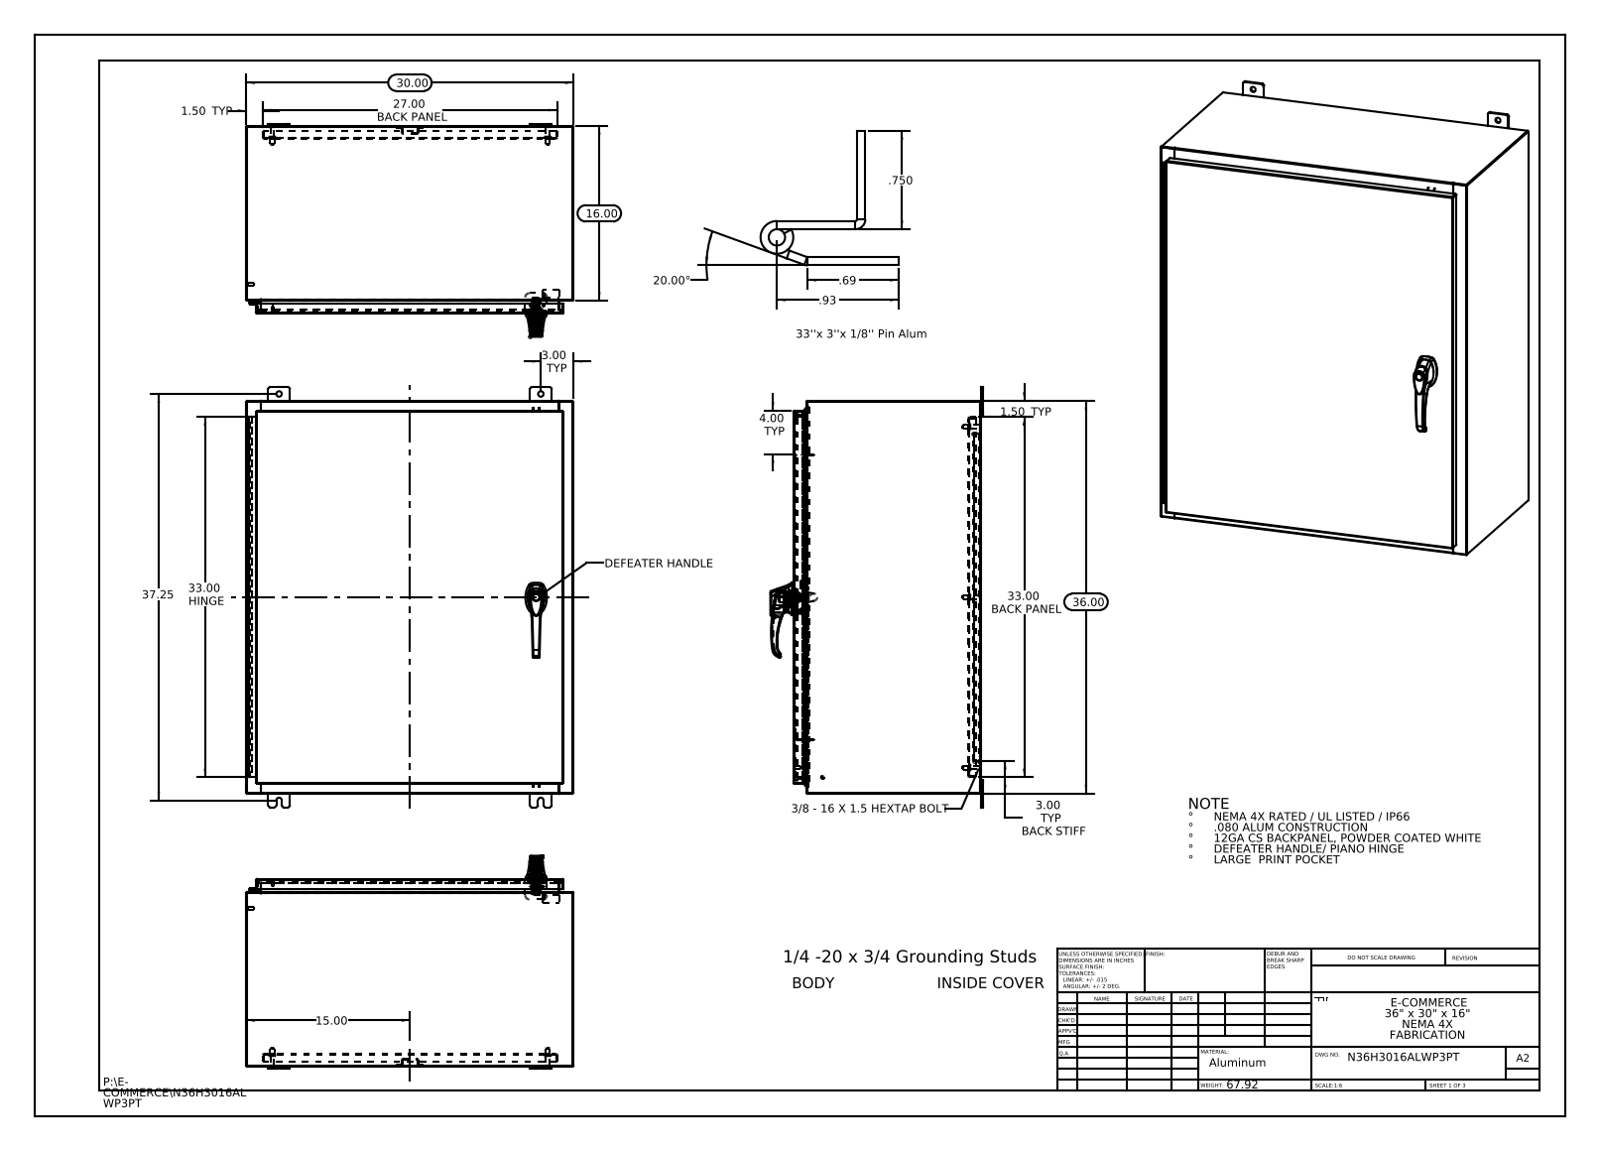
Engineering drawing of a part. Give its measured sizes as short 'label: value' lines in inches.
name: 297025; N36H3016ALWP3PT Body; N36H3016ALWP3PT 125 Pin Hinge; NMP-SS-RODGUIDES (+8 more)
written by: SolidWorks 2013 (CONFIG_CONTROL_DESIGN)
unit: in
bodies: 40 solids, 2894 faces (1083 planar, 1093 cylindrical, 718 other)
size: 38.5 × 30 × 19.495
volume: 467.9 in³; area: 11 711 in²
holes: 10× ⌀0.5, 4× ⌀0.25, 3× ⌀0.138, 3× ⌀0.161, 2× ⌀0.079, 2× ⌀0.203, 2× ⌀0.313, 2× ⌀0.437, 1× ⌀0.125, 1× ⌀0.125, 1× ⌀0.197, 1× ⌀0.276
bosses: 6× ⌀0.625, 6× ⌀0.375, 6× ⌀0.33, 4× ⌀0.157, 4× ⌀0.14, 3× ⌀0.315, 3× ⌀0.236, 1× ⌀1.181
rounds: 37× R0.118, 33× R0.006, 28× R0.013, 24× R0.19, 22× R0.088, 15× R0.039, 12× R0.028, 6× R0.008
face distances: 0.075, 17.126, 29.925, 17.051, 0.104, 17.201, 35.925, 1, 16.126, 1.075
hole spacings: 11.363, 13.669, 15.625, 29.694, 25.25, 28.129, 0.295, 0.625
